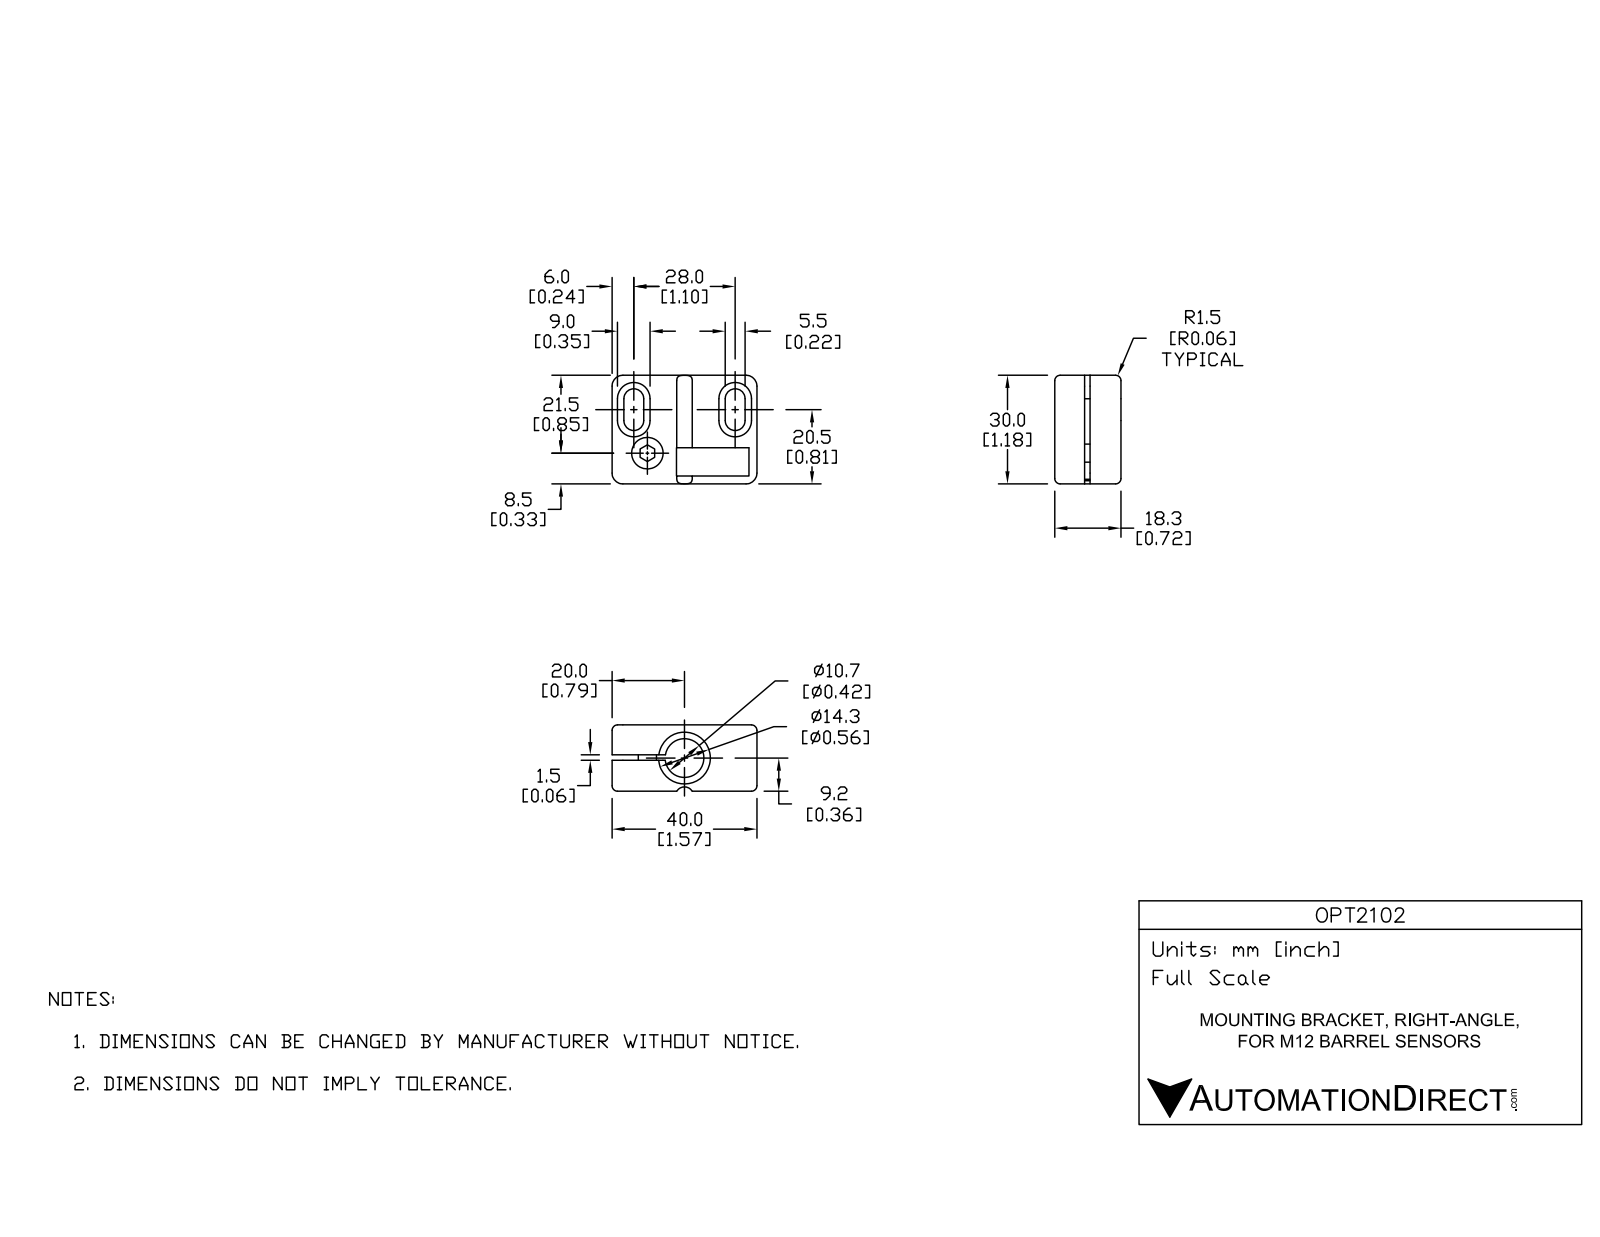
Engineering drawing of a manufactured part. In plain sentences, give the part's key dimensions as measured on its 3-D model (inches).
The part is named "56 10 20 12". Its 3-D file was written by "Unknown (AUTOMOTIVE_DESIGN)". It is 1 solid with 75 faces: 34 planar, 30 cylindrical and 11 other. Overall it measures 1.575 by 1.181 by 0.72 inches. Its volume is 0.857 cubic inches and its surface area 11.7 square inches. Round holes: 1 of diameter 0.217, 1 of diameter 0.343, 1 of diameter 0.421, 1 of diameter 0.472. Round bosses or shafts: 1 of diameter 0.335, 1 of diameter 0.197. Partial cylindrical surfaces (rounded edges, fillets, slot ends): 8 of radius 0.059, 4 of radius 0.108, 4 of radius 0.118, 4 of radius 0.177, 1 of radius 0.098. The main face-to-face distances are 0.059, 0.337, 0.72, 0.325, 0.396, 1.181, 0.384, 1.575, 0.069, 0.285.
